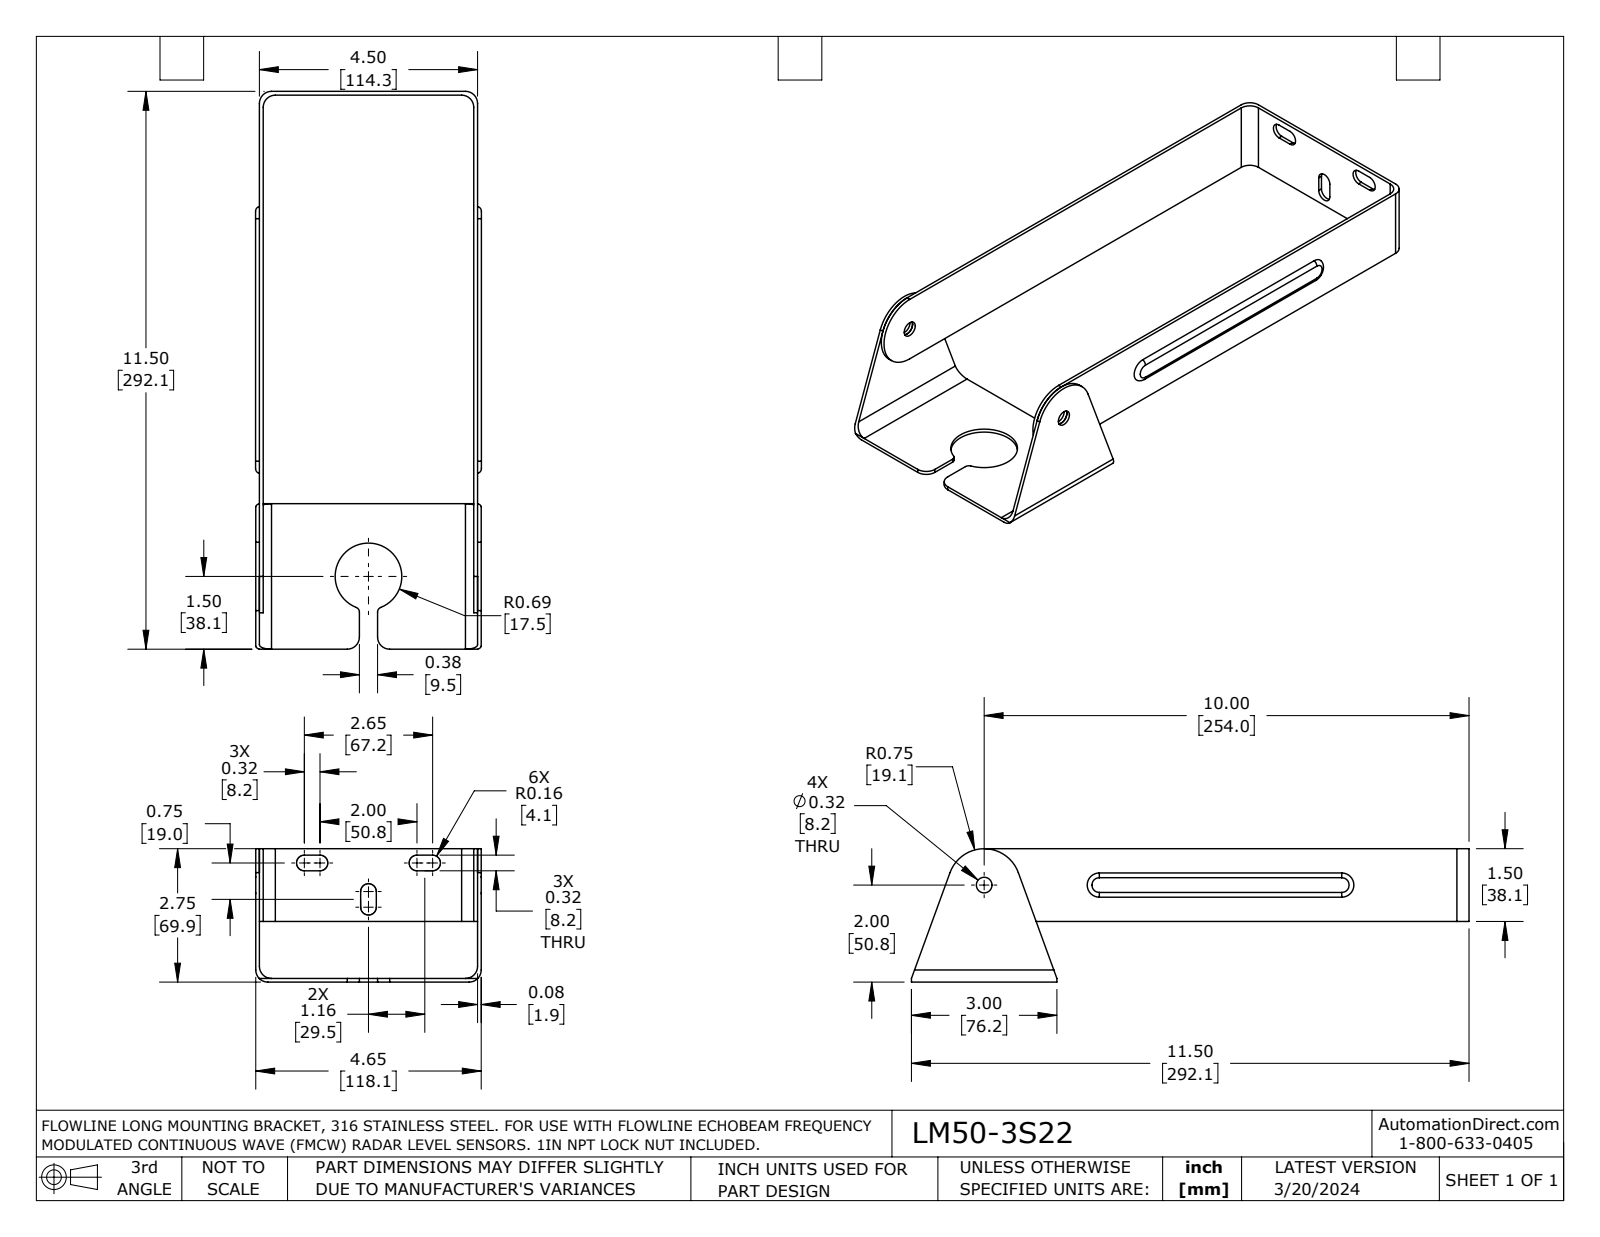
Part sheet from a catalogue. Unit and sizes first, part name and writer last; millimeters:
Units: millimetres
Overall size (bounding box): 292.1 × 118.3 × 69.9
Round holes (diameter × count): ⌀8.2 ×1, ⌀34.9 ×1
Partial cylindrical surfaces — rounded edges, fillets, slot ends (radius × count): R6.4 ×10, R2.5 ×6, R4.1 ×6, R19.1 ×1
Main face-to-face distances: 2, 112.3, 114.3, 1.9, 110.3, 3.9, 114.2, 116.2, 118.1, 4
Volume: 82 440 mm³ · Surface area: 81 420 mm²
Bodies: 2 solids, 75 faces (31 planar, 38 cylindrical, 6 other)
Part name (STEP PRODUCT): LM50-3S22
STEP written by: SolidWorks 2021 (AUTOMOTIVE_DESIGN)
